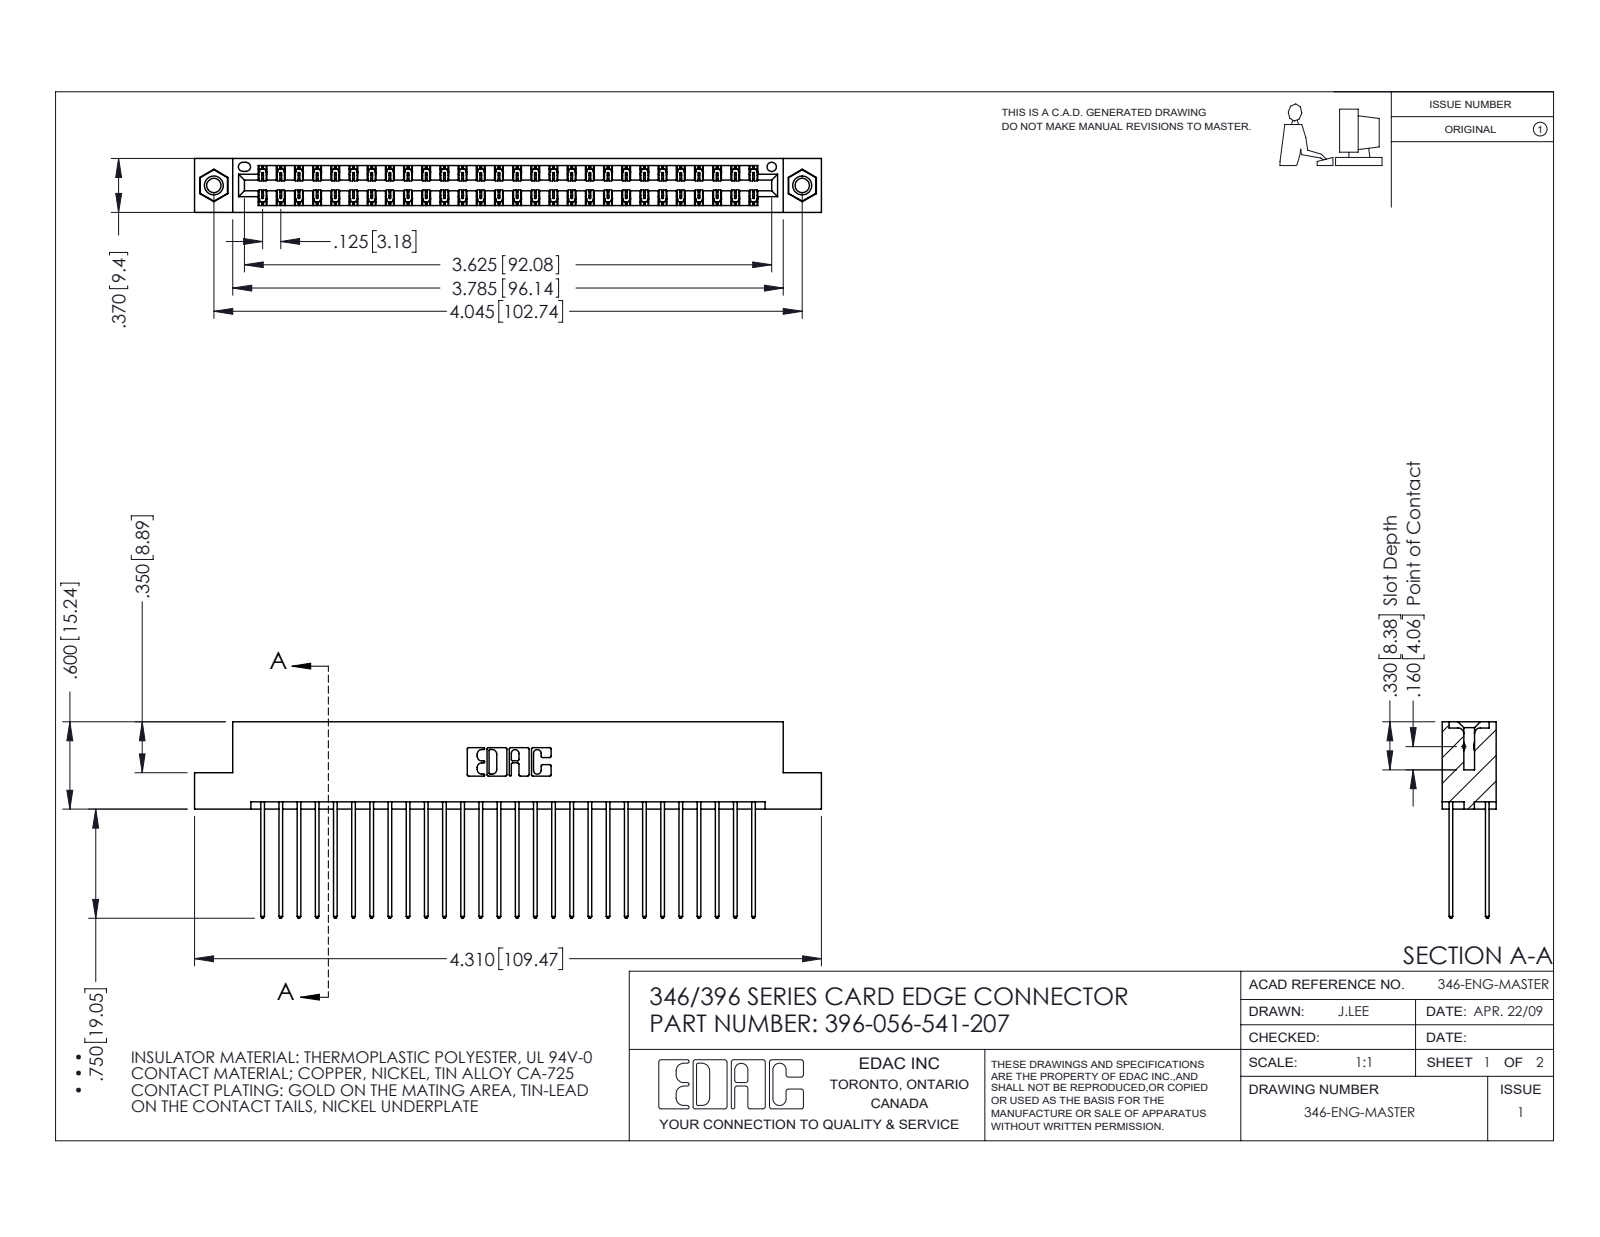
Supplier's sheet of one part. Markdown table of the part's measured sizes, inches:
| quantity | value |
| --- | --- |
| part name | 346 Part_Flush Mounting Lugs - 0.156 Dia-TI; 345-292-001_345-293-141; 396-056-541-207; 345-250-001_345-250-005-103 |
| STEP written by | SolidWorks 2016 (CONFIG_CONTROL_DESIGN) |
| units | inches |
| bodies | 59 solids, 3094 faces (2068 planar, 1010 cylindrical, 16 other) |
| overall size | 4.31 × 1.35 × 0.37 |
| volume | 0.664 in³ |
| surface area | 25.27 in² |
| round holes (diameter × count) | 0.098 × 2, 0.125 × 2, 0.156 × 2, 0.064 × 1 |
| round bosses / shafts (diameter × count) | 0.155 × 2 |
| partial cylindrical surfaces (radius × count) | 0.006 × 84, 0.01 × 56, 0.01 × 22, 0.007 × 6, 0.031 × 6, 0.026 × 3, 0.014 × 2, 0.022 × 2 |
| main face-to-face distances | 0.048, 0.322, 0.25, 0.072, 0.298, 0.025, 0.37, 0.275, 0.225, 0.148 |
| hole center spacings | 0.246, 3.837, 4.045 |
